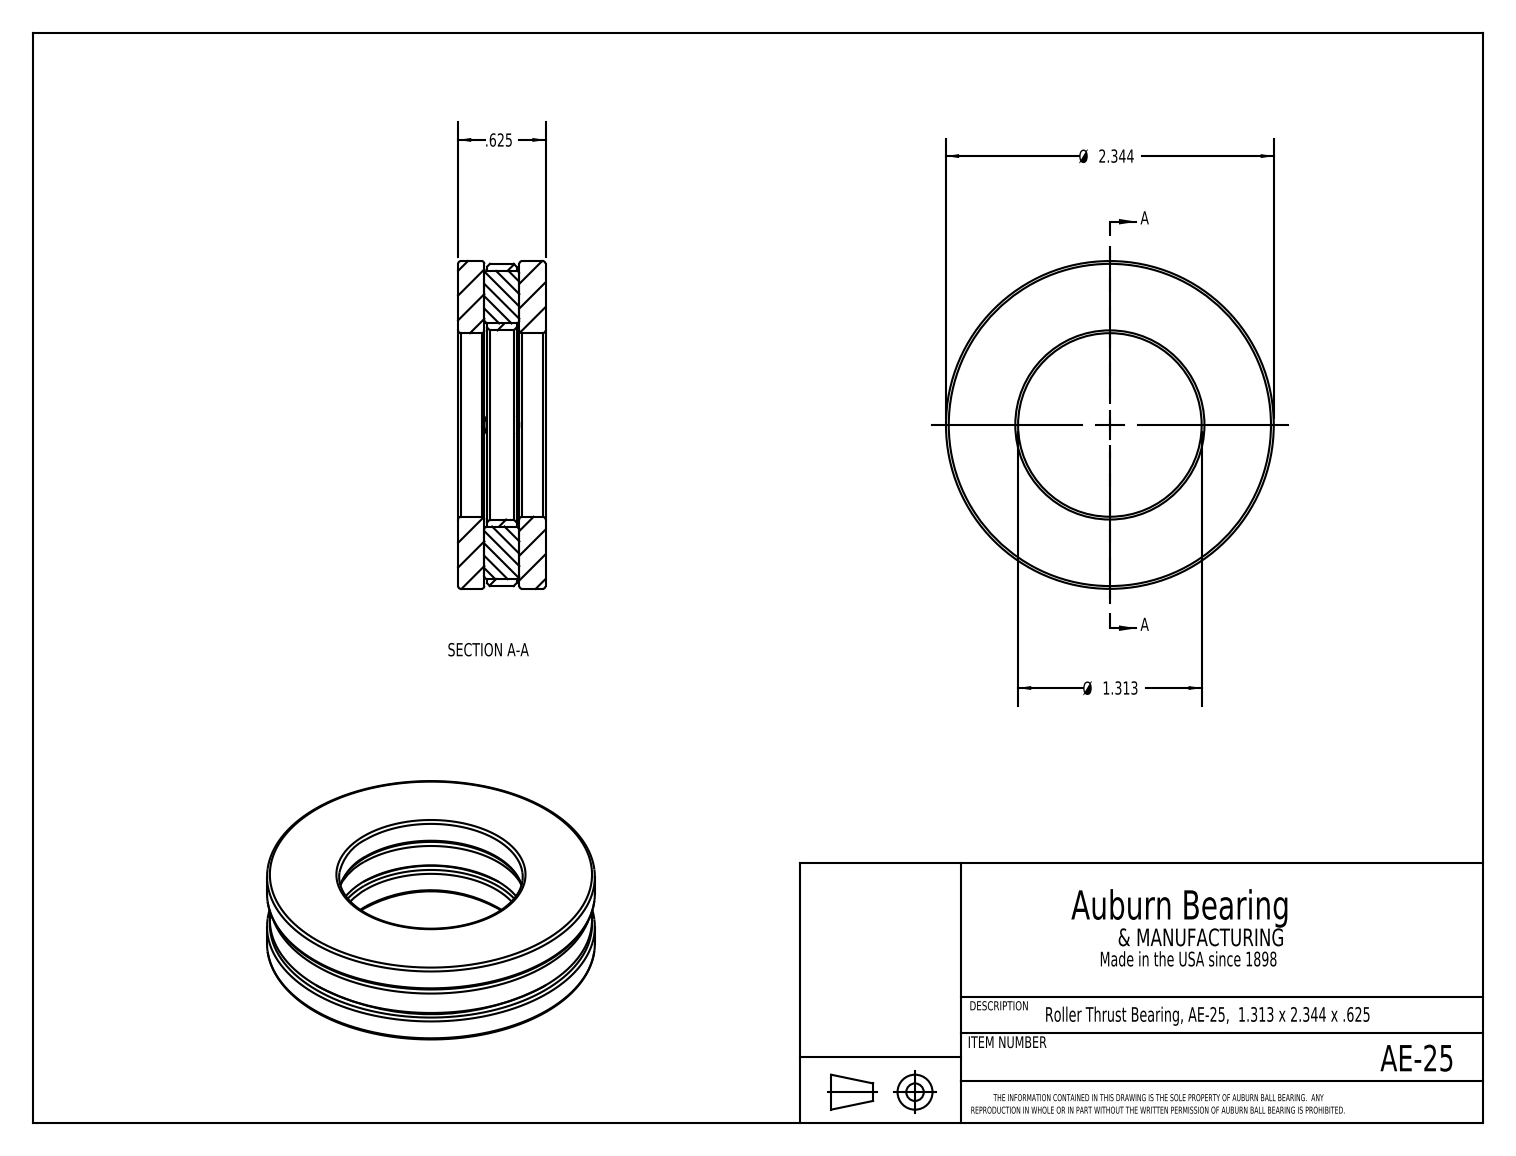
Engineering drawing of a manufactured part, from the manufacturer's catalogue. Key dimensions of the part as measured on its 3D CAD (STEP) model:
Part name (STEP PRODUCT): AE-25
STEP written by: SolidWorks 2017 (CONFIG_CONTROL_DESIGN)
Units: inches
Bodies: 7 solids, 60 faces (30 planar, 10 cylindrical, 20 other)
Overall size (bounding box): 2.344 × 2.344 × 0.625
Volume: 1.67 in³ · Surface area: 25.18 in²
Round holes (diameter × count): ⌀1.313 ×1, ⌀1.353 ×1
Round bosses / shafts (diameter × count): ⌀0.25 ×2, ⌀2.344 ×1, ⌀2.304 ×1
Main face-to-face distances: 0.207, 0.418, 0.25, 0.187, 0.437, 0.625, 0.438, 0.188, 0.23, 0.02
